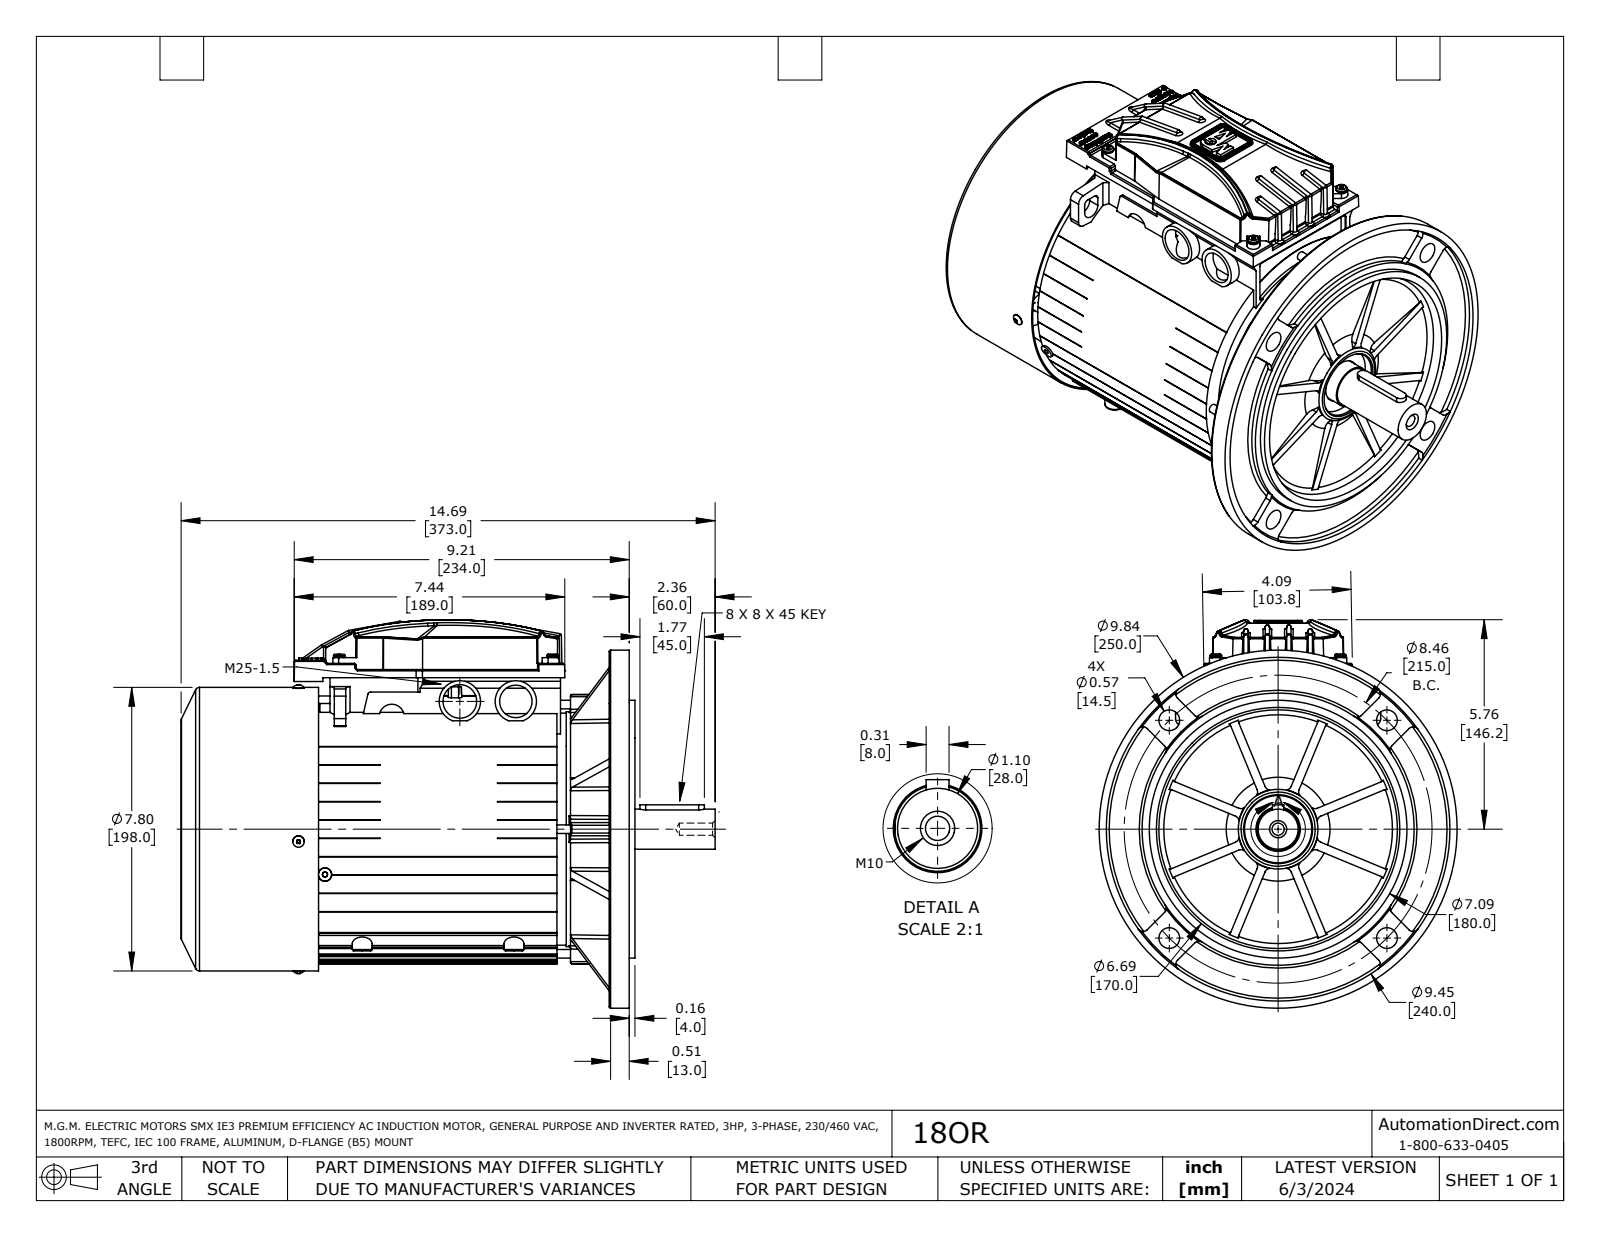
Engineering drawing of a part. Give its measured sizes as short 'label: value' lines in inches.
name: 18OR
written by: SolidWorks 2021 (AUTOMOTIVE_DESIGN)
unit: in
bodies: 14 solids, 3863 faces (1553 planar, 1291 cylindrical, 1019 other)
size: 14.685 × 10.679 × 9.843
volume: 357.7 in³; area: 1 195 in²
holes: 7× ⌀0.13, 7× ⌀0.177, 5× ⌀0.098, 5× ⌀0.315, 4× ⌀0.15, 4× ⌀0.157, 4× ⌀0.197, 4× ⌀0.256, 4× ⌀0.354, 4× ⌀0.571, 2× ⌀0.118, 1× ⌀0.335
bosses: 8× ⌀0.315, 6× ⌀0.138, 4× ⌀0.236, 4× ⌀0.079, 3× ⌀0.276, 2× ⌀1.138, 1× ⌀9.843, 1× ⌀7.795
rounds: 540× R0.039, 101× R0.157, 48× R0.016, 47× R0.059, 32× R0.008, 24× R0.004, 22× R0.079, 20× R0.031
face distances: 0.197, 1.319, 10.256, 1.732, 6.811, 8.74, 8.13, 8.327, 10.472, 10.059
hole spacings: 3.024, 3.033, 4.886, 7.081, 7.135, 3.425, 0.059, 3.484
